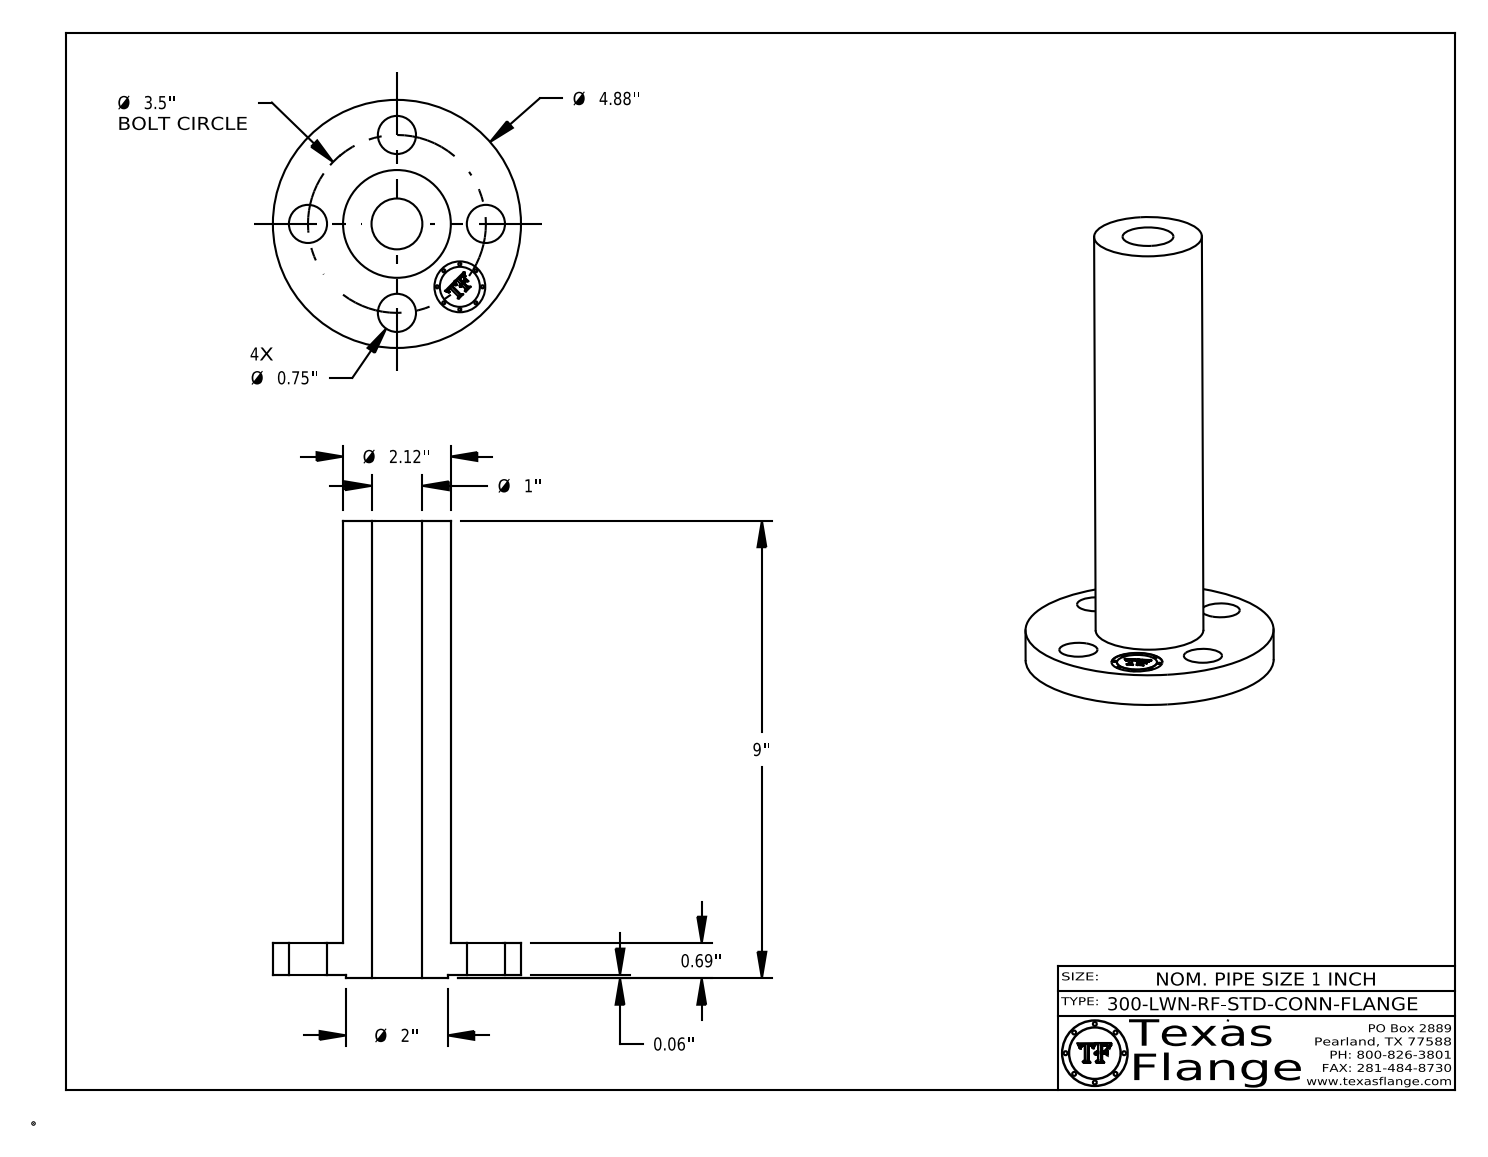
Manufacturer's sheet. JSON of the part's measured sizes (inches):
{"part_name": "1-300-LWN-RF-STD-CONN-FLANGE", "step_written_by": "CATIA V5 STEP AP214 (AUTOMOTIVE_DESIGN)", "units": "inches", "bodies": {"solids": 1, "faces": 405, "planar": 369, "cylindrical": 36, "other": 0}, "overall_size": [9, 4.88, 4.88], "volume_in3": 33.09, "surface_area_in2": 131.9, "round_holes": [[0.75, 4], [1, 2]], "round_bosses_or_shafts": [[0.061, 8], [4.88, 1], [2.12, 1], [2, 1], [0.788, 1]], "face_to_face_distances": [0.628, 8.937, 8.31, 0.063, 0.69, 9, 0.685, 0.622, 8.315, 0.298], "hole_center_spacings": [1.75, 2.475, 1.339, 3.233, 3.5]}
